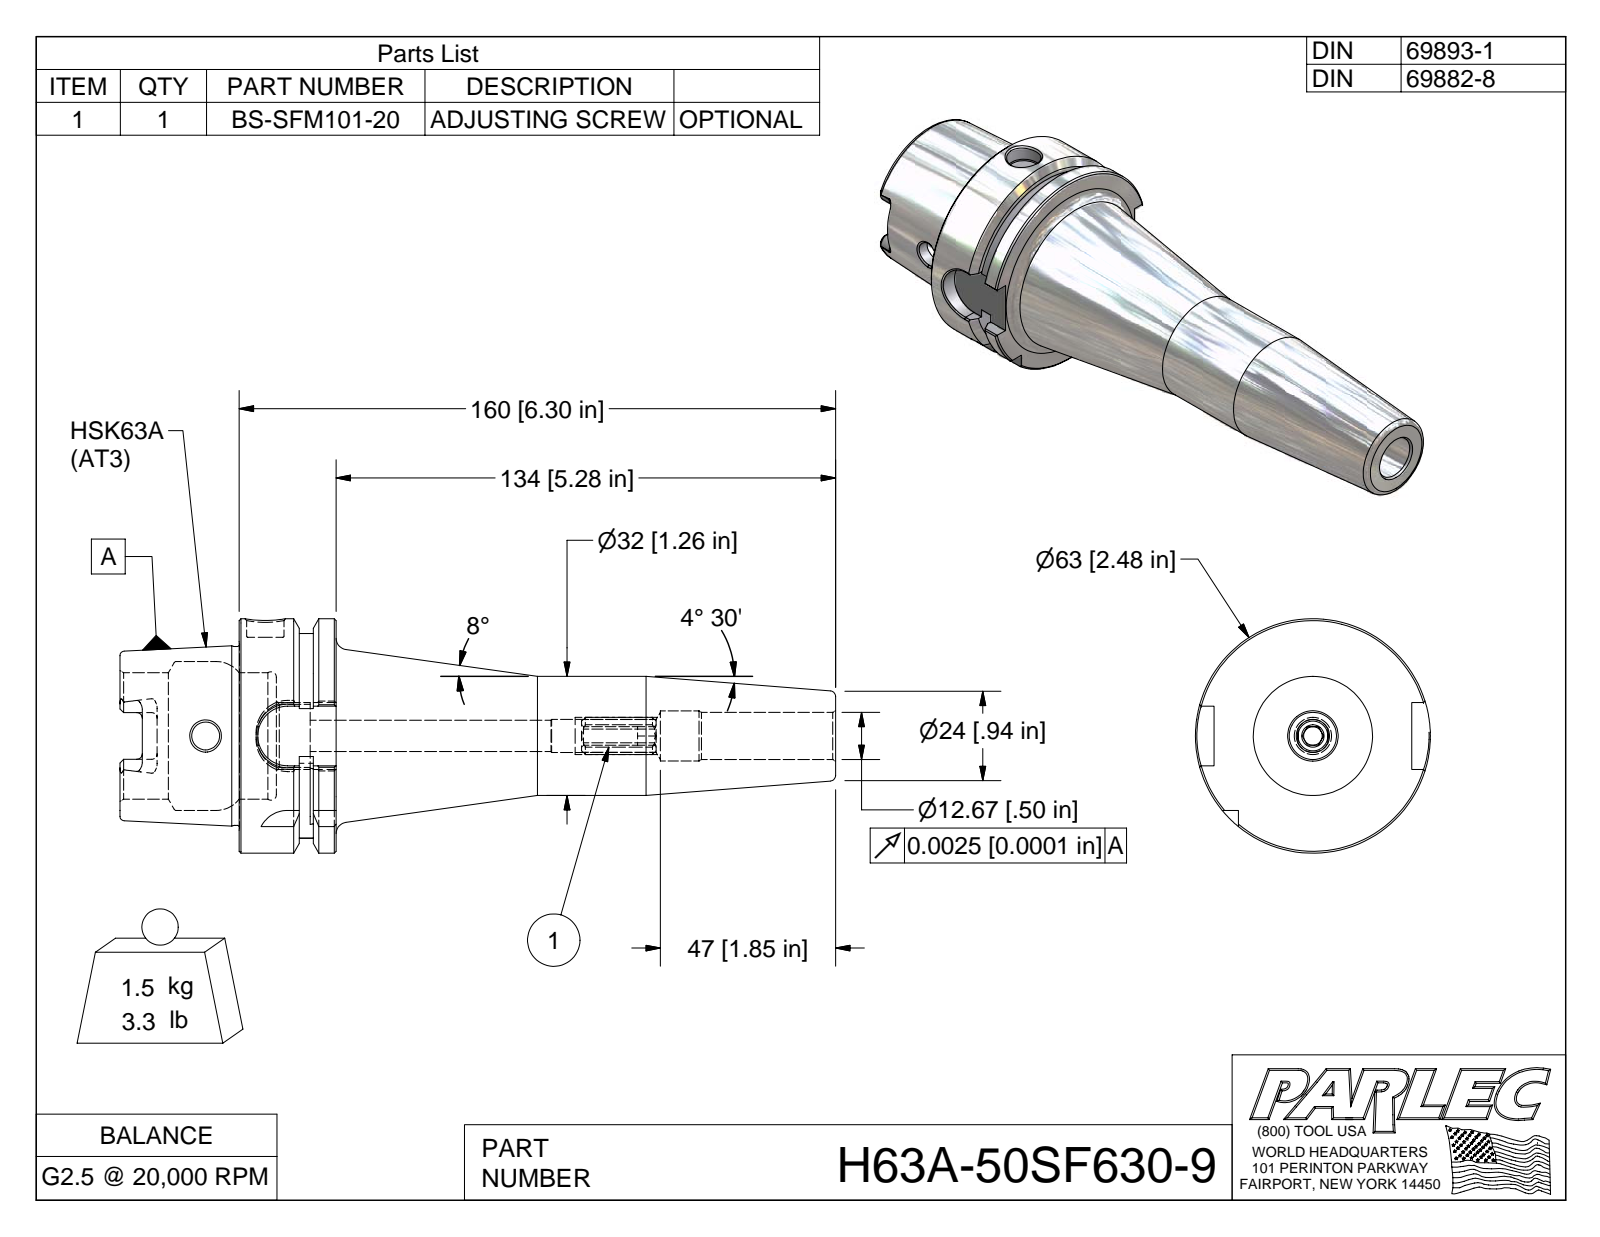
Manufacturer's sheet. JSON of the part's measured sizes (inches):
{"part_name": "H63A-50SF630-9; H63A-50SF630-9-1; BS-SFM101-20", "step_written_by": "Autodesk Inventor 2009 (AUTOMOTIVE_DESIGN)", "units": "inches", "bodies": {"solids": 2, "faces": 160, "planar": 59, "cylindrical": 35, "other": 66}, "overall_size": [7.559, 2.48, 2.48], "volume_in3": 11.84, "surface_area_in2": 62.39, "round_holes": [[0.295, 1], [0.394, 1], [0.499, 1], [0.529, 1], [0.666, 1], [1.339, 1], [1.575, 1]], "round_bosses_or_shafts": [[2.48, 1], [1.891, 1], [1.26, 1]], "partial_cylinders_radius": [[0.059, 6], [0.113, 4], [0.315, 4], [0.197, 1], [1.083, 1]], "face_to_face_distances": [1.024, 0.241, 0.389, 0.63, 0.394, 1.26, 1.654, 2.283, 1.894, 0.635]}
